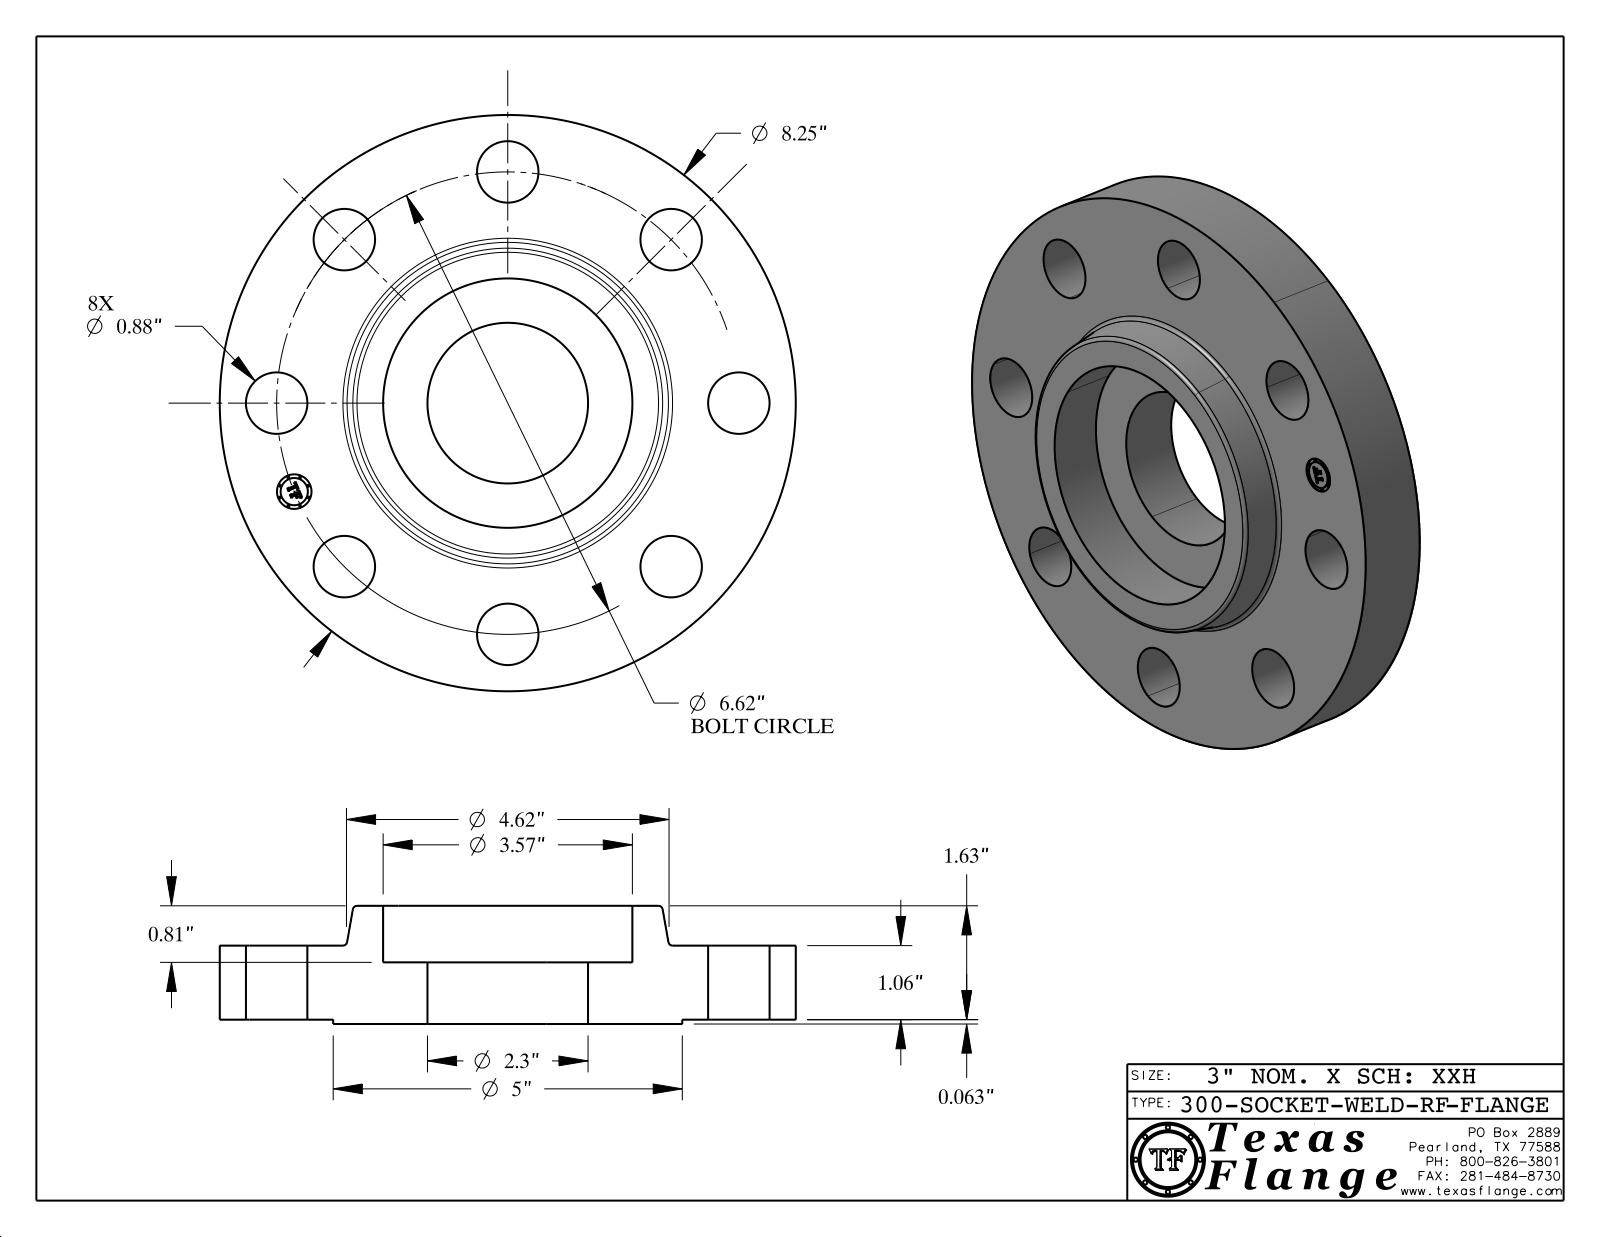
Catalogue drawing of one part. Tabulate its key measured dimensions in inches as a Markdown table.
| quantity | value |
| --- | --- |
| part name | 300-SOCKET-WELD-RF |
| STEP written by | CATIA V5 STEP AP214 (AUTOMOTIVE_DESIGN) |
| units | inches |
| bodies | 1 solid, 420 faces (370 planar, 44 cylindrical, 6 other) |
| overall size | 8.25 × 8.25 × 1.693 |
| volume | 50.1 in³ |
| surface area | 162.6 in² |
| round holes (diameter × count) | 0.88 × 8, 0.495 × 1, 2.3 × 1, 3.57 × 1 |
| round bosses / shafts (diameter × count) | 0.03 × 8, 8.25 × 1, 5 × 1, 0.39 × 1 |
| main face-to-face distances | 1.06, 0.063, 1.122, 0.883, 0.82, 0.24, 1.693, 1.63, 0.81, 0.57 |
| hole center spacings | 3.31, 2.533, 6.116, 4.681, 4.681, 1.291, 3.678, 6.493 |
